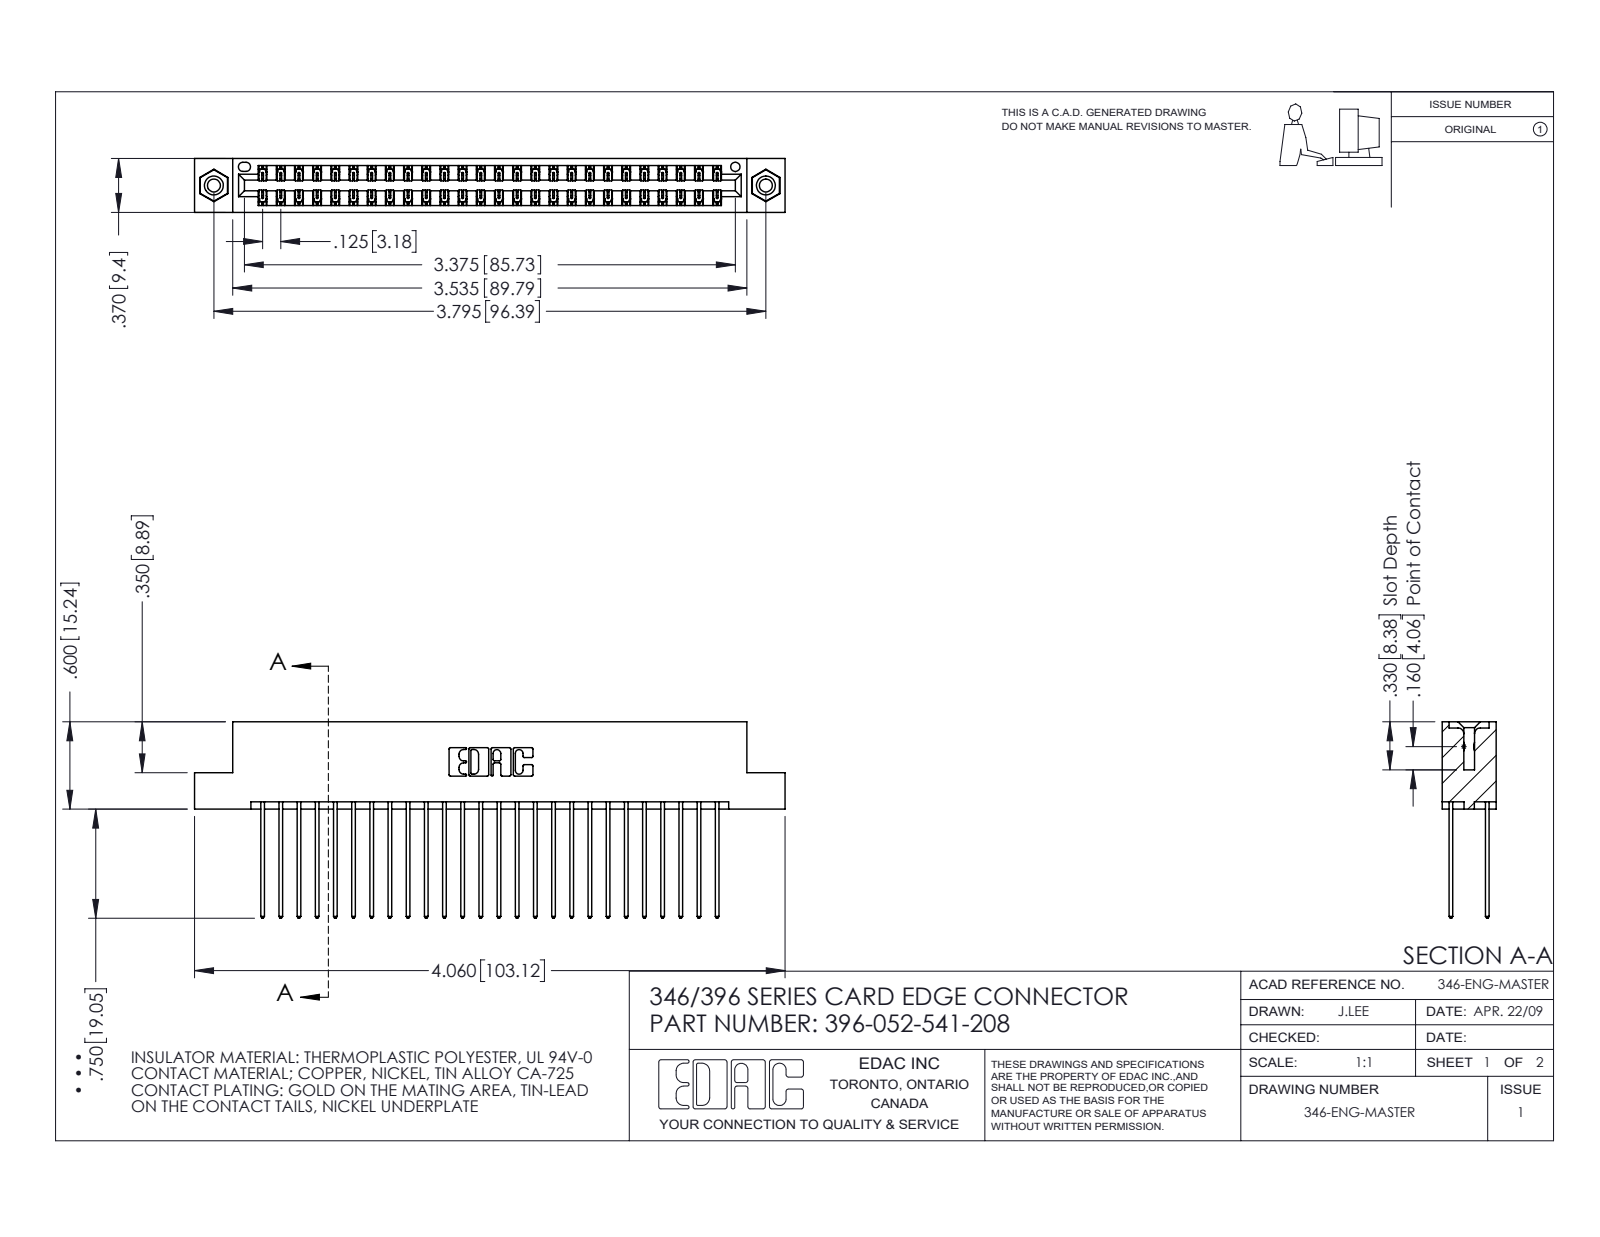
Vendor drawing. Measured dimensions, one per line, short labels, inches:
name: 396-052-541-208; 345-250-001_345-250-003-102; 345-292-001_345-293-141; 346 Part_Flush Mounting Lugs - 0.156 Dia-TI
written by: SolidWorks 2016 (CONFIG_CONTROL_DESIGN)
unit: in
bodies: 55 solids, 2886 faces (1928 planar, 942 cylindrical, 16 other)
size: 4.06 × 1.35 × 0.37
volume: 0.624 in³; area: 23.64 in²
holes: 2× ⌀0.089, 2× ⌀0.125, 2× ⌀0.156, 1× ⌀0.064
bosses: 2× ⌀0.155
rounds: 78× R0.006, 52× R0.01, 22× R0.01, 6× R0.007, 6× R0.031, 3× R0.026, 2× R0.014, 2× R0.022
face distances: 0.048, 0.322, 0.25, 0.072, 0.298, 0.025, 0.37, 0.275, 0.225, 0.148
hole spacings: 0.246, 3.587, 3.795
